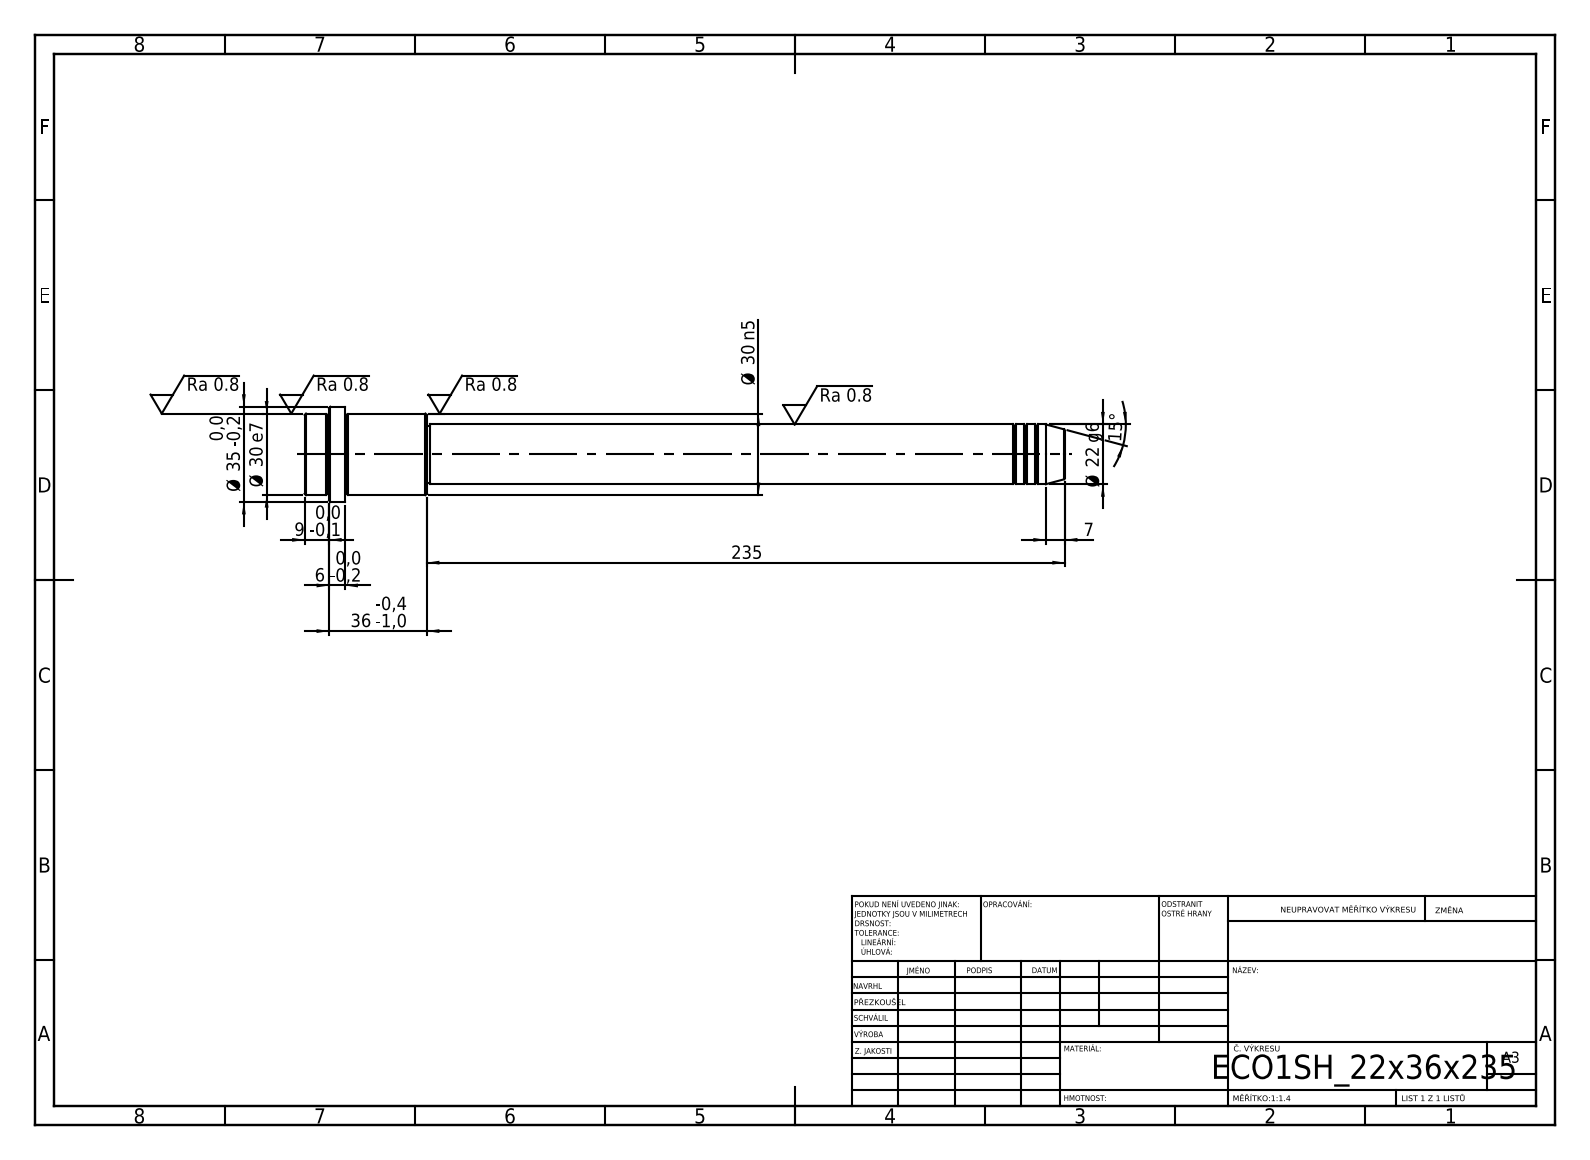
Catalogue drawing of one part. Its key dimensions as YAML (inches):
step_written_by: "SolidWorks 2019 (CONFIG_CONTROL_DESIGN)"
units: inches
bodies: {solids: 1, faces: 52, planar: 6, cylindrical: 16, other: 30}
overall_size: [11.024, 1.378, 1.378]
volume: 7.446
surface_area: 34.93
round_bosses_or_shafts:
  - {diameter: 1.378, count: 1}
  - {diameter: 1.181, count: 1}
  - {diameter: 0.866, count: 1}
  - {diameter: 0.827, count: 1}
face_to_face_distances: [1.772, 1.181, 0.591, 9.252, 10.433, 11.024, 10.669, 1.417, 0.236, 0.354]
